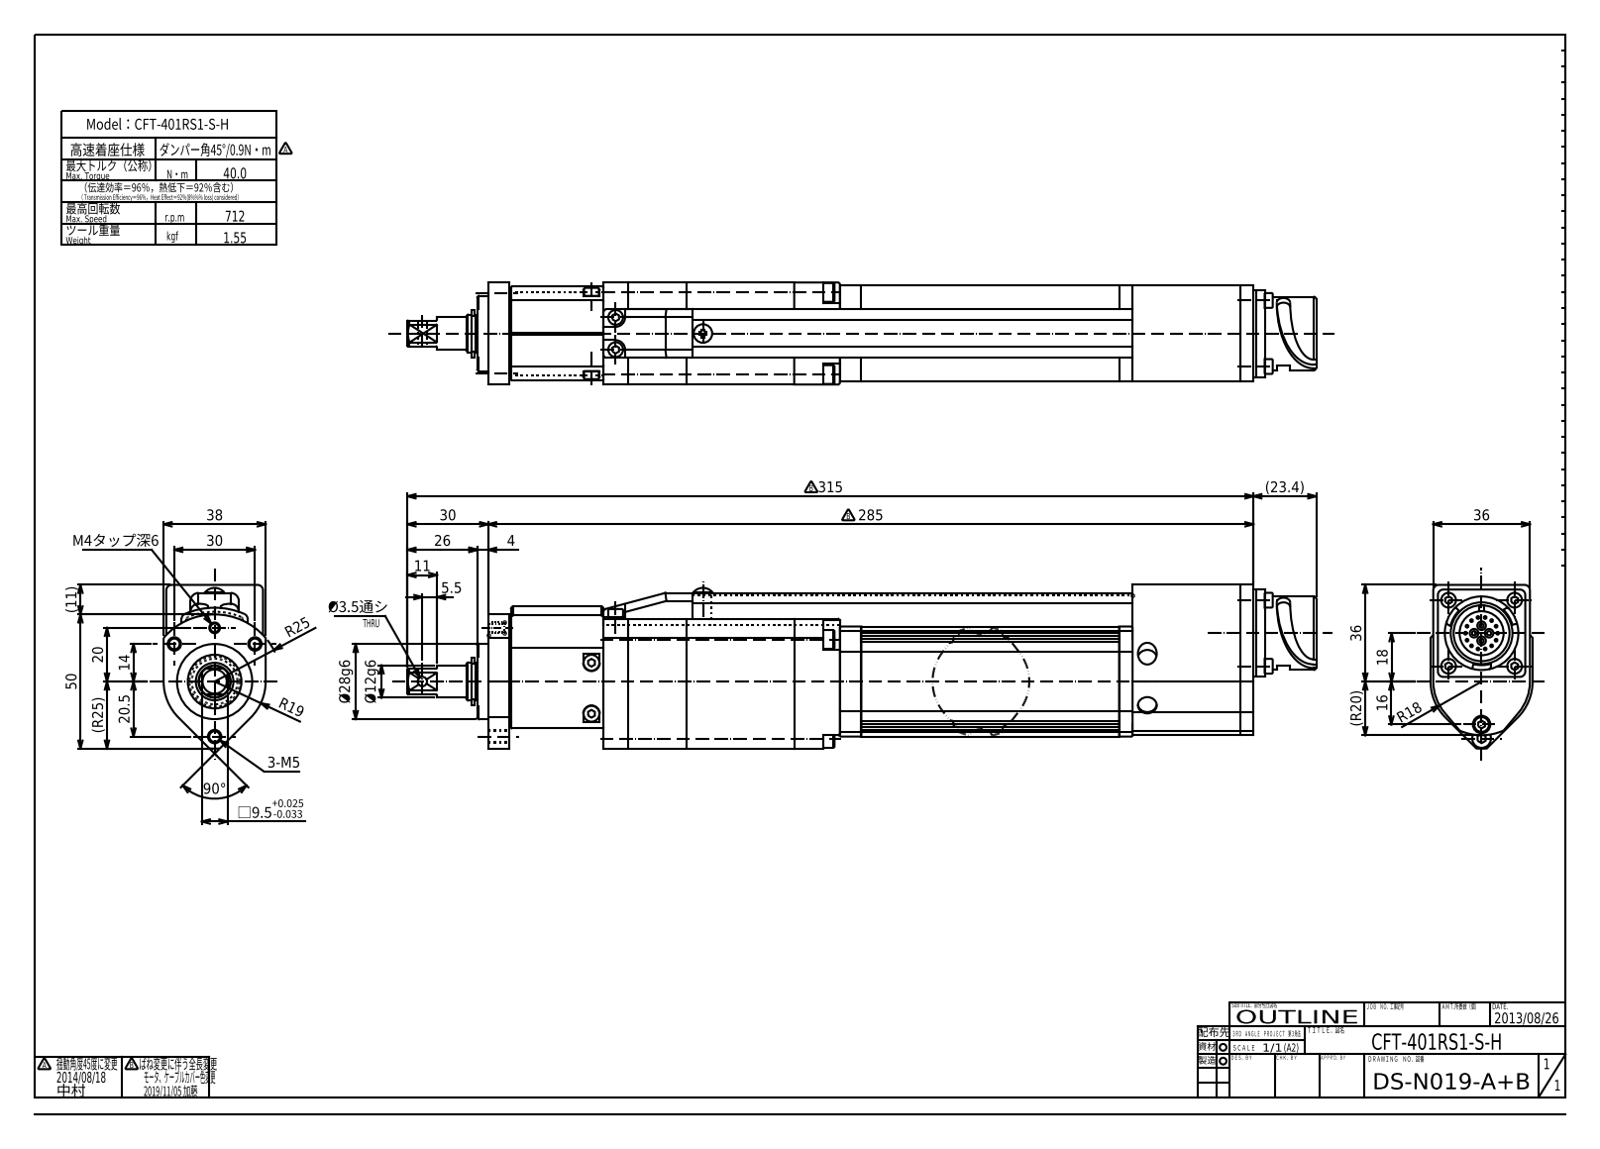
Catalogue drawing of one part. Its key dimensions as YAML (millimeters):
part_name: "CFT-401RS1-S-H(DS-N019+F)_OUTLINE_20201118"
step_written_by: "Autodesk Inventor 2021 (AUTOMOTIVE_DESIGN)"
units: millimeters
bodies: {solids: 1, faces: 700, planar: 436, cylindrical: 188, other: 76}
overall_size: [338.4, 61, 38]
volume: 438498
surface_area: 59895
round_holes:
  - {diameter: 3.24, count: 4}
  - {diameter: 4.13, count: 3}
  - {diameter: 1.2, count: 2}
  - {diameter: 7, count: 2}
  - {diameter: 3.5, count: 1}
  - {diameter: 6.5, count: 1}
  - {diameter: 14.7, count: 1}
  - {diameter: 20.8, count: 1}
round_bosses_or_shafts:
  - {diameter: 1, count: 14}
  - {diameter: 5.5, count: 11}
  - {diameter: 1.6, count: 4}
  - {diameter: 7, count: 3}
  - {diameter: 6, count: 2}
  - {diameter: 4.5, count: 2}
  - {diameter: 30, count: 1}
  - {diameter: 28, count: 1}
partial_cylinders:
  - {radius: 3, count: 7}
  - {radius: 0.3, count: 6}
  - {radius: 2, count: 6}
  - {radius: 2.75, count: 6}
  - {radius: 4, count: 5}
  - {radius: 0.5, count: 4}
  - {radius: 3.25, count: 4}
  - {radius: 1, count: 3}
face_to_face_distances: [1, 10, 27, 9, 28, 37, 36, 3, 0.5, 18]
hole_center_spacings: [16.16, 0.85, 7.76, 10.7, 12.67, 14.53, 15.17, 15.52]
